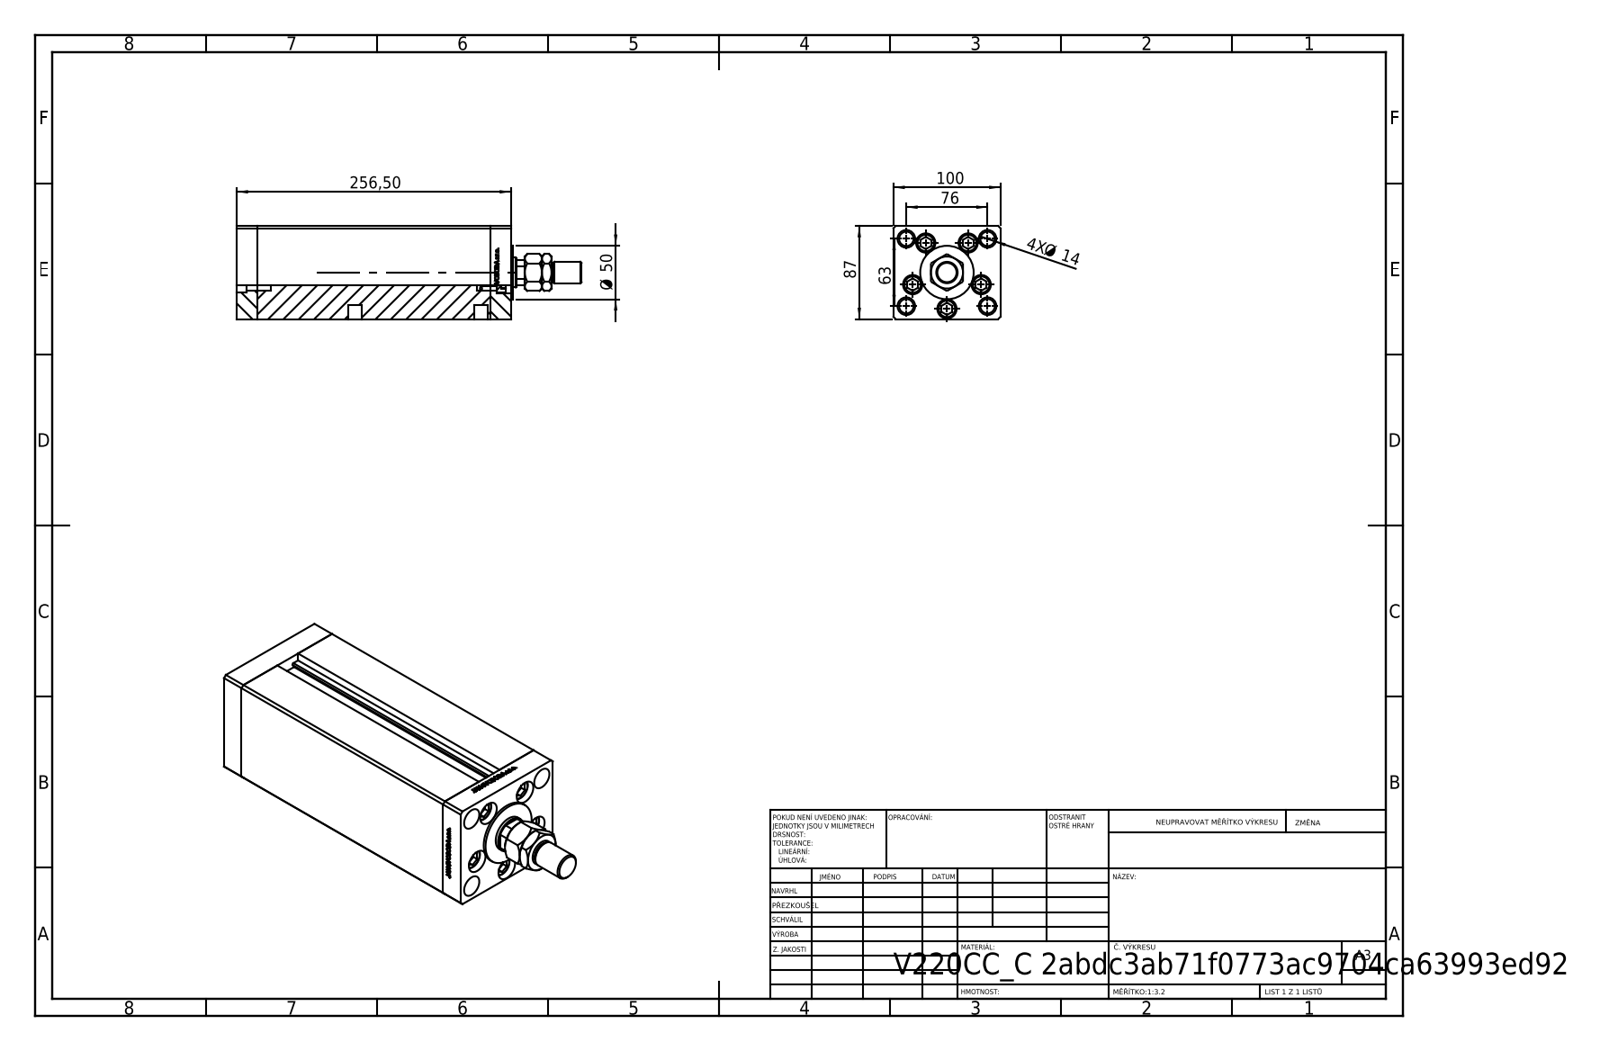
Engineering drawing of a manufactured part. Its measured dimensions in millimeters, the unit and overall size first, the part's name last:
Units: millimetres
Overall size (bounding box): 322.5 × 100 × 87
Round holes (diameter × count): ⌀13.5 ×9, ⌀18 ×5, ⌀2 ×4, ⌀12 ×4, ⌀13.16 ×4, ⌀16.5 ×4, ⌀17 ×1, ⌀18.5 ×1, ⌀28 ×1
Round bosses / shafts (diameter × count): ⌀8 ×5, ⌀17 ×4, ⌀50 ×1, ⌀20 ×1, ⌀18 ×1
Partial cylindrical surfaces — rounded edges, fillets, slot ends (radius × count): R0.93 ×2, R13.5 ×1
Main face-to-face distances: 100, 87, 19, 218.5, 237.5, 34.25, 256.5, 222.25, 203.25, 15.25
Hole centre spacings: 34, 49.36, 18.59, 21.03, 38.08, 39.27, 40.83, 43.24
Volume: 1 848 000 mm³ · Surface area: 285 330 mm²
Bodies: 14 solids, 1235 faces (563 planar, 180 cylindrical, 492 other)
Part name (STEP PRODUCT): V220C_C MIDDLE; MTA; V220C FRONT; V220C_VC_C (+2 more)
STEP written by: SolidWorks 2019 (CONFIG_CONTROL_DESIGN)
